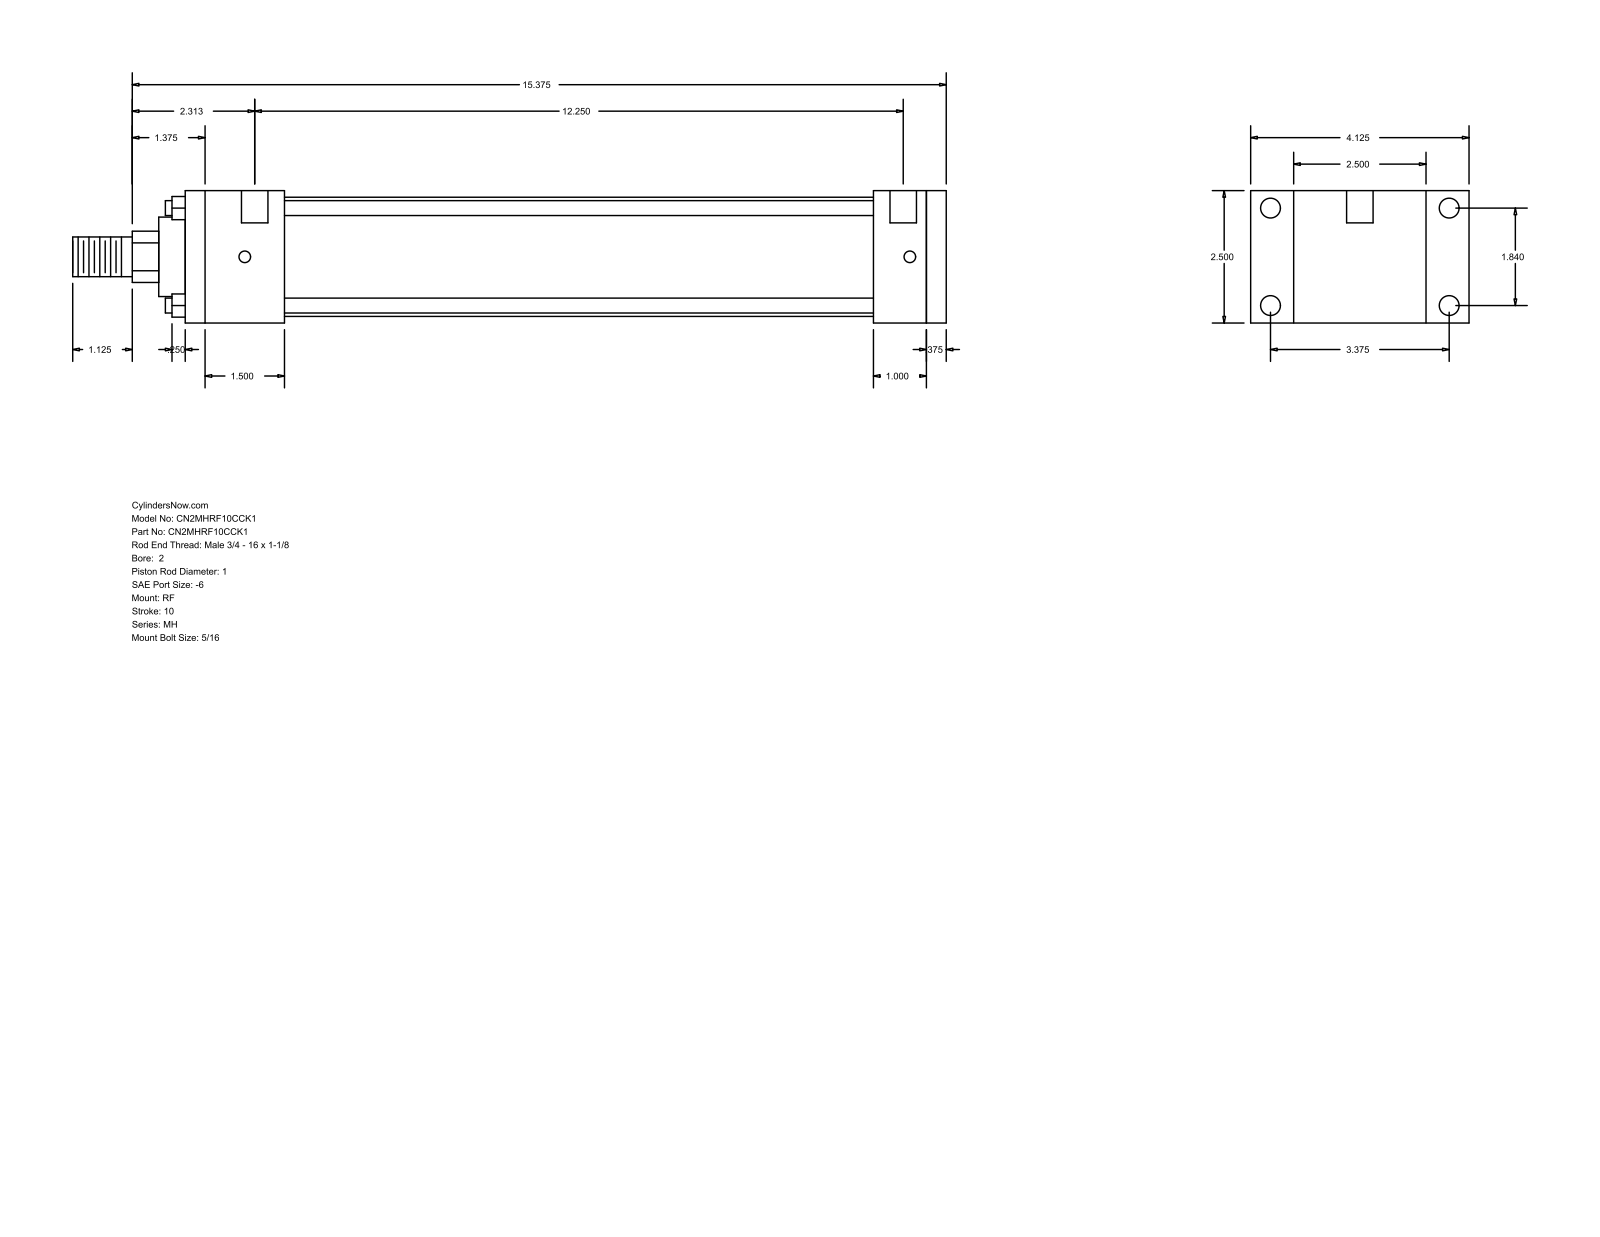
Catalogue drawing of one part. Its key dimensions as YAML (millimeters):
part_name: "MH_RF__0200_1"
step_written_by: "GSSL Pune (CONFIG_CONTROL_DESIGN)"
units: millimeters
bodies: {solids: 0, faces: 92, planar: 64, cylindrical: 28, other: 0}
overall_size: [419.1, 104.78, 63.5]
round_holes:
  - {diameter: 5.56, count: 4}
  - {diameter: 9.53, count: 4}
  - {diameter: 12.7, count: 2}
round_bosses_or_shafts:
  - {diameter: 7.14, count: 4}
  - {diameter: 57.15, count: 1}
  - {diameter: 38.1, count: 1}
  - {diameter: 25.4, count: 1}
  - {diameter: 19.05, count: 1}
partial_cylinders:
  - {radius: 12.29, count: 1}
face_to_face_distances: [63.5, 365.12, 9.52, 355.6, 20.64, 25.4, 47.63, 330.2, 282.57, 307.97]
hole_center_spacings: [46.74, 85.72, 97.63, 319.08, 3.17, 4.76, 311.15, 314.32]
